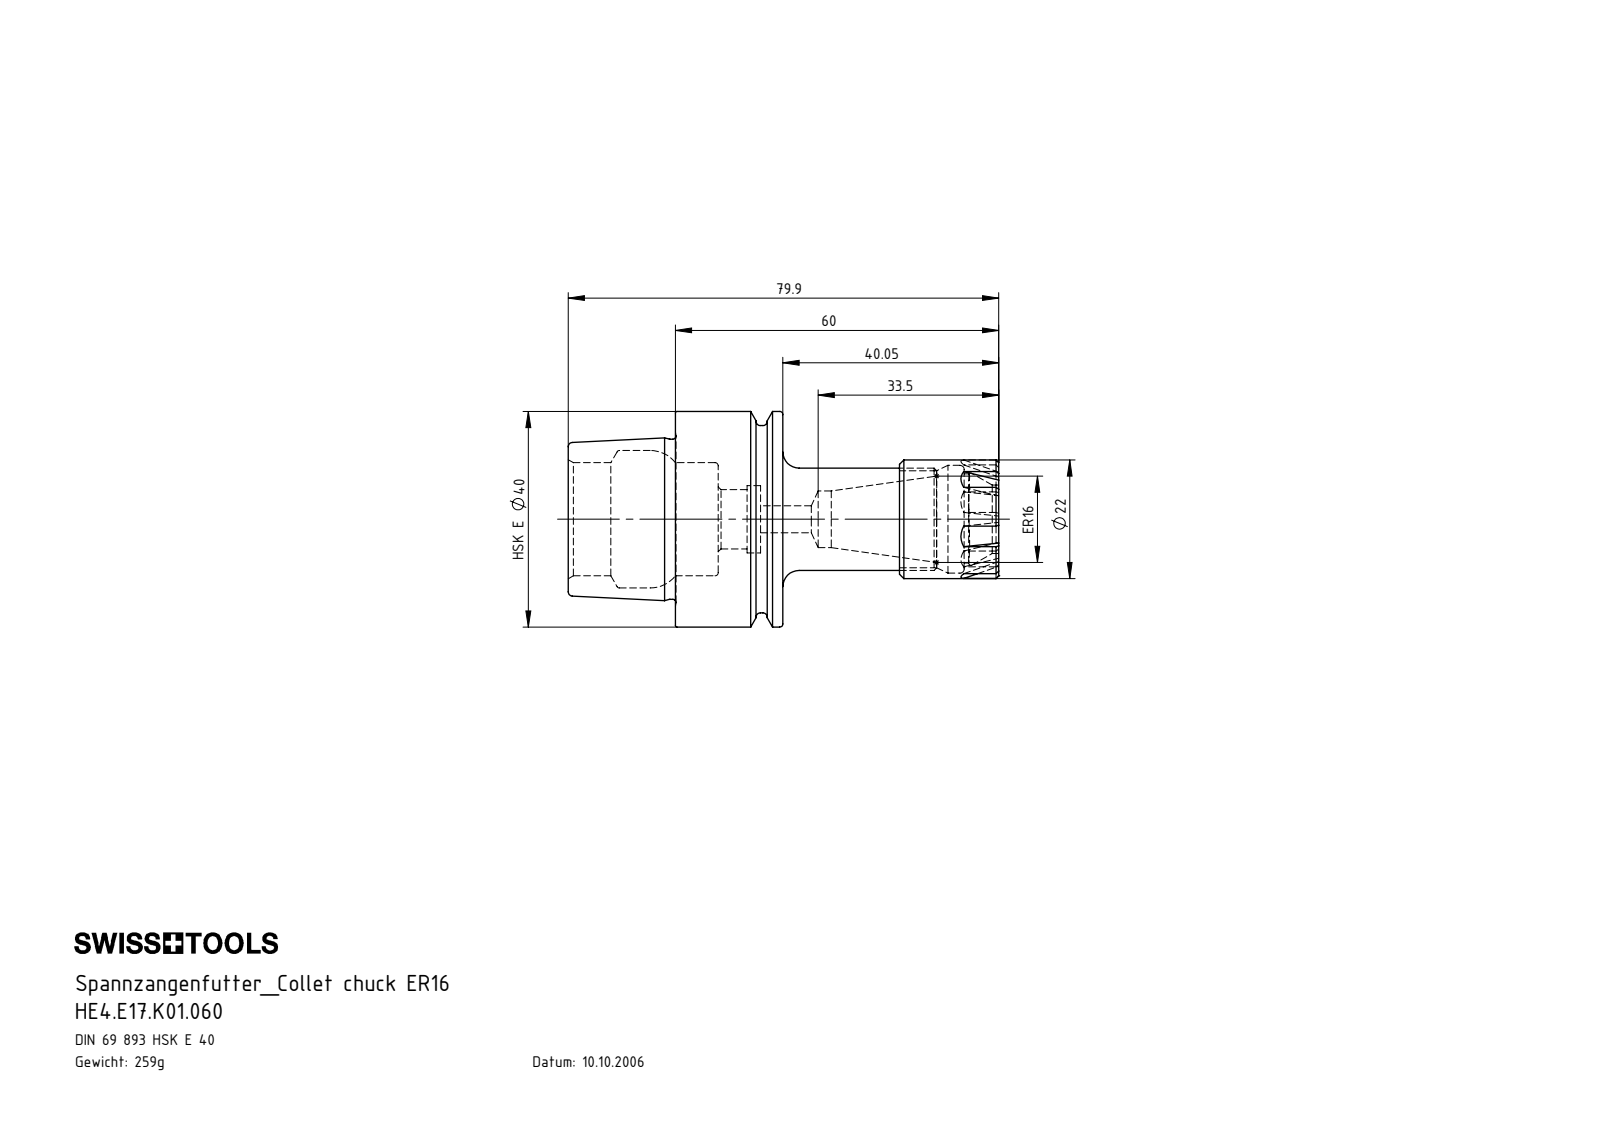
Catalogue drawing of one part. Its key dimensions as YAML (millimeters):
part_name: "E17-ER1.001.018; HE4-E17.K01.060_A_Fertigbearbeitung; HE4.E17.K01.060"
step_written_by: "SolidWorks 2017 (CONFIG_CONTROL_DESIGN)"
units: millimeters
bodies: {solids: 2, faces: 131, planar: 33, cylindrical: 35, other: 63}
overall_size: [79.9, 40, 40]
volume: 32983
surface_area: 14738
round_holes:
  - {diameter: 5, count: 1}
  - {diameter: 10.5, count: 1}
  - {diameter: 11, count: 1}
  - {diameter: 12.5, count: 1}
  - {diameter: 12.7, count: 1}
  - {diameter: 18, count: 1}
  - {diameter: 20, count: 1}
  - {diameter: 21, count: 1}
  - {diameter: 25.5, count: 1}
round_bosses_or_shafts:
  - {diameter: 40, count: 1}
  - {diameter: 34.75, count: 1}
  - {diameter: 29.71, count: 1}
  - {diameter: 22, count: 1}
  - {diameter: 19, count: 1}
partial_cylinders:
  - {radius: 7.7, count: 2}
face_to_face_distances: [19.95, 12, 7.95, 19.9, 27.85, 39.85, 79.9, 60, 52.05, 40.05]
